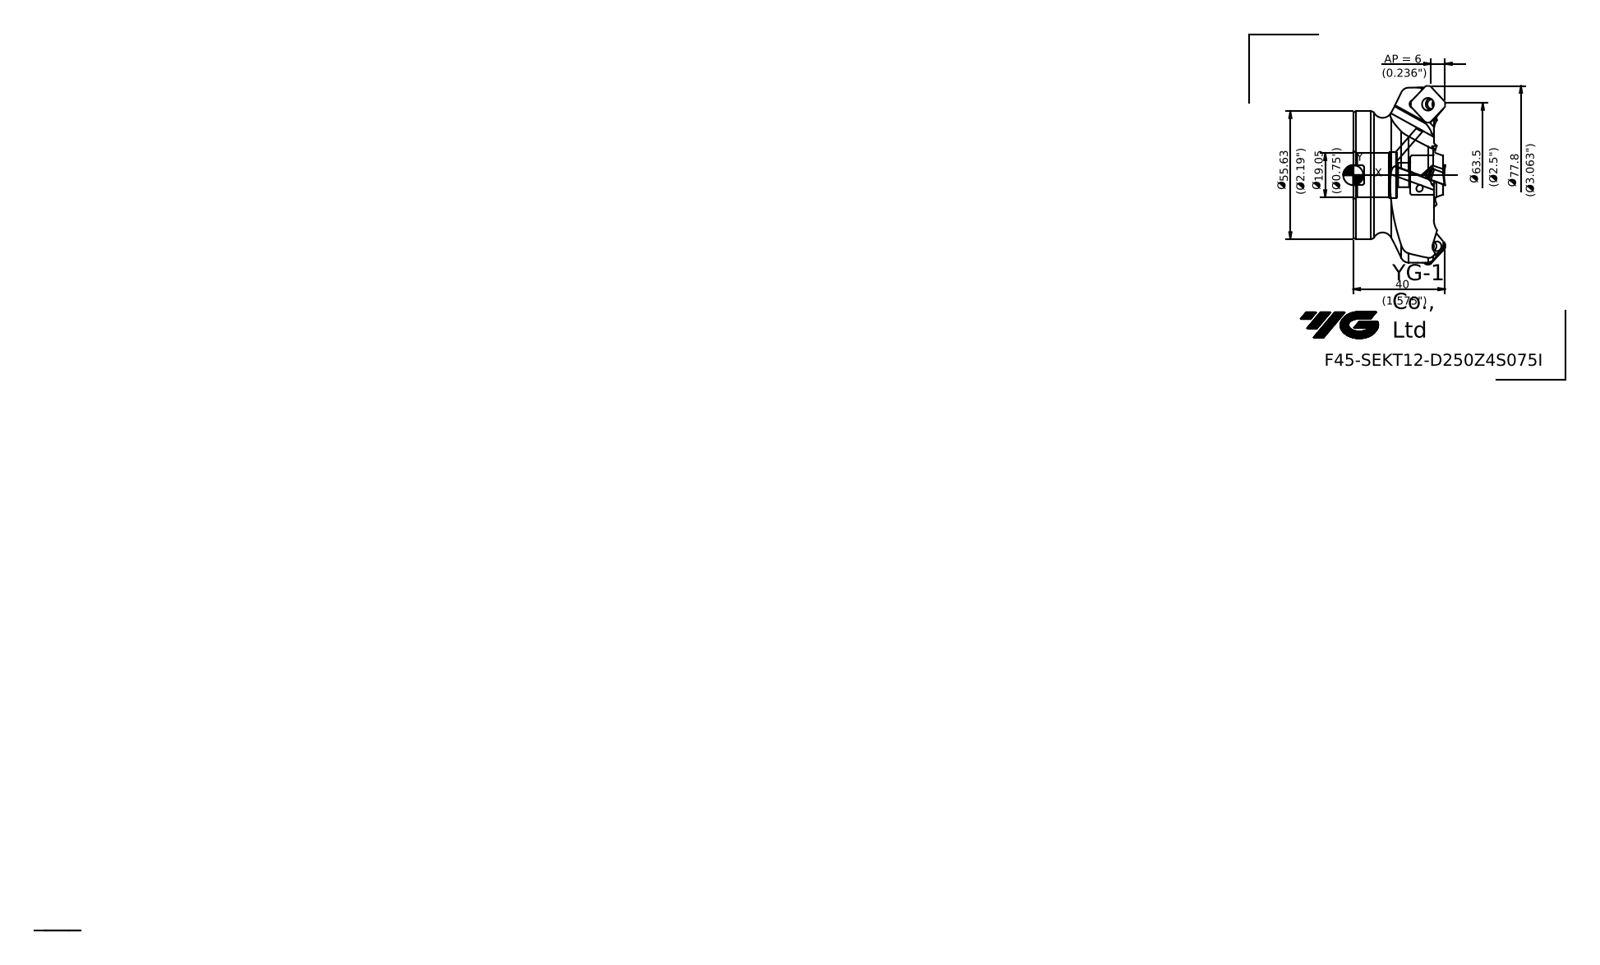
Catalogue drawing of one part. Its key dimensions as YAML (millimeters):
part_name: "10223BA0B540cm4l"
step_written_by: "SIEMENS PLM Software NX 10.0 (AP203_CONFIGURATION_CONTROLLED_3D_DESIGN_OF_MECHANICAL_PARTS_AND_ASSEMBLIES_MIM_LF)"
units: millimeters
bodies: {solids: 1, faces: 66, planar: 15, cylindrical: 9, other: 42}
overall_size: [77.8, 77.8, 40]
volume: 111036
surface_area: 26659
round_holes:
  - {diameter: 10.49, count: 1}
  - {diameter: 17, count: 1}
  - {diameter: 19.05, count: 1}
  - {diameter: 19.85, count: 1}
round_bosses_or_shafts:
  - {diameter: 55.63, count: 1}
partial_cylinders:
  - {radius: 0.8, count: 2}
face_to_face_distances: [35.09, 30.34, 4.75, 16.04, 14.3, 19.05, 8.35, 10.3, 5.74, 20.04]
